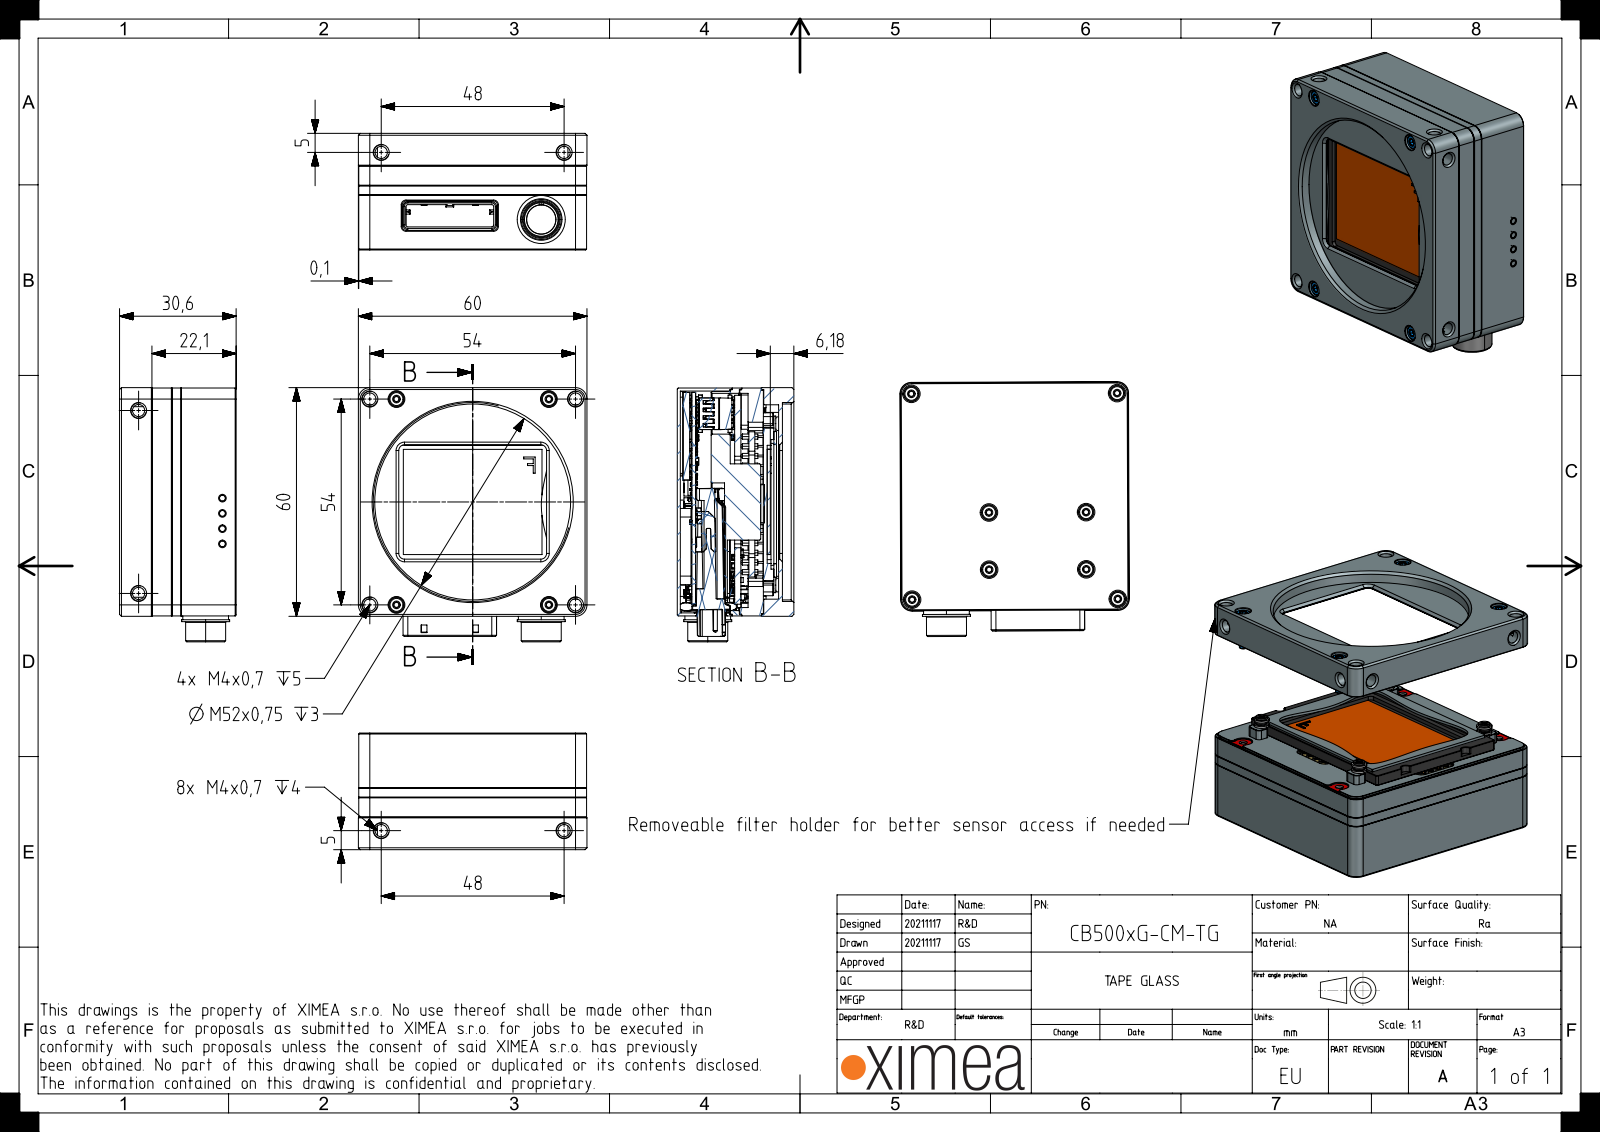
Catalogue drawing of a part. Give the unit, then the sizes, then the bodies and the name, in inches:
Units: inches
Overall size (bounding box): 2.626 × 2.362 × 1.205
Round holes (diameter × count): ⌀0.053 ×141, ⌀0.063 ×28, ⌀0.083 ×19, ⌀0.024 ×12, ⌀0.051 ×12, ⌀0.079 ×12, ⌀0.161 ×12, ⌀0.126 ×8, ⌀0.039 ×5, ⌀0.061 ×4, ⌀0.098 ×4, ⌀0.185 ×4
Round bosses / shafts (diameter × count): ⌀0.018 ×140, ⌀0.15 ×12, ⌀0.016 ×12, ⌀0.118 ×10, ⌀0.075 ×7, ⌀0.158 ×4, ⌀0.064 ×4, ⌀0.033 ×4
Partial cylindrical surfaces — rounded edges, fillets, slot ends (radius × count): R0.004 ×127, R0.039 ×67, R0.011 ×60, R0.02 ×55, R0.012 ×53, R0.118 ×46, R0.008 ×34, R0.006 ×32
Main face-to-face distances: 0.118, 0.031, 0.157, 0.039, 0.15, 0.898, 0.657, 0.547, 0.89, 0.74
Hole centre spacings: 0.1, 0.141, 0.2, 0.055, 0.224, 0.3, 0.316, 0.4
Volume: 3.502 in³ · Surface area: 128.1 in²
Bodies: 294 solids, 27562 faces (21231 planar, 4453 cylindrical, 1878 other)
Part name (STEP PRODUCT): CONN-074540-0400; CBX4L-MAIN-PCA-4A-LW; SROB-M1.6X4-TX-STNLS; MECH-CBX4-REAR (+8 more)
STEP written by: SIEMENS PLM Software NX 1907 (AUTOMOTIVE_DESIGN)
